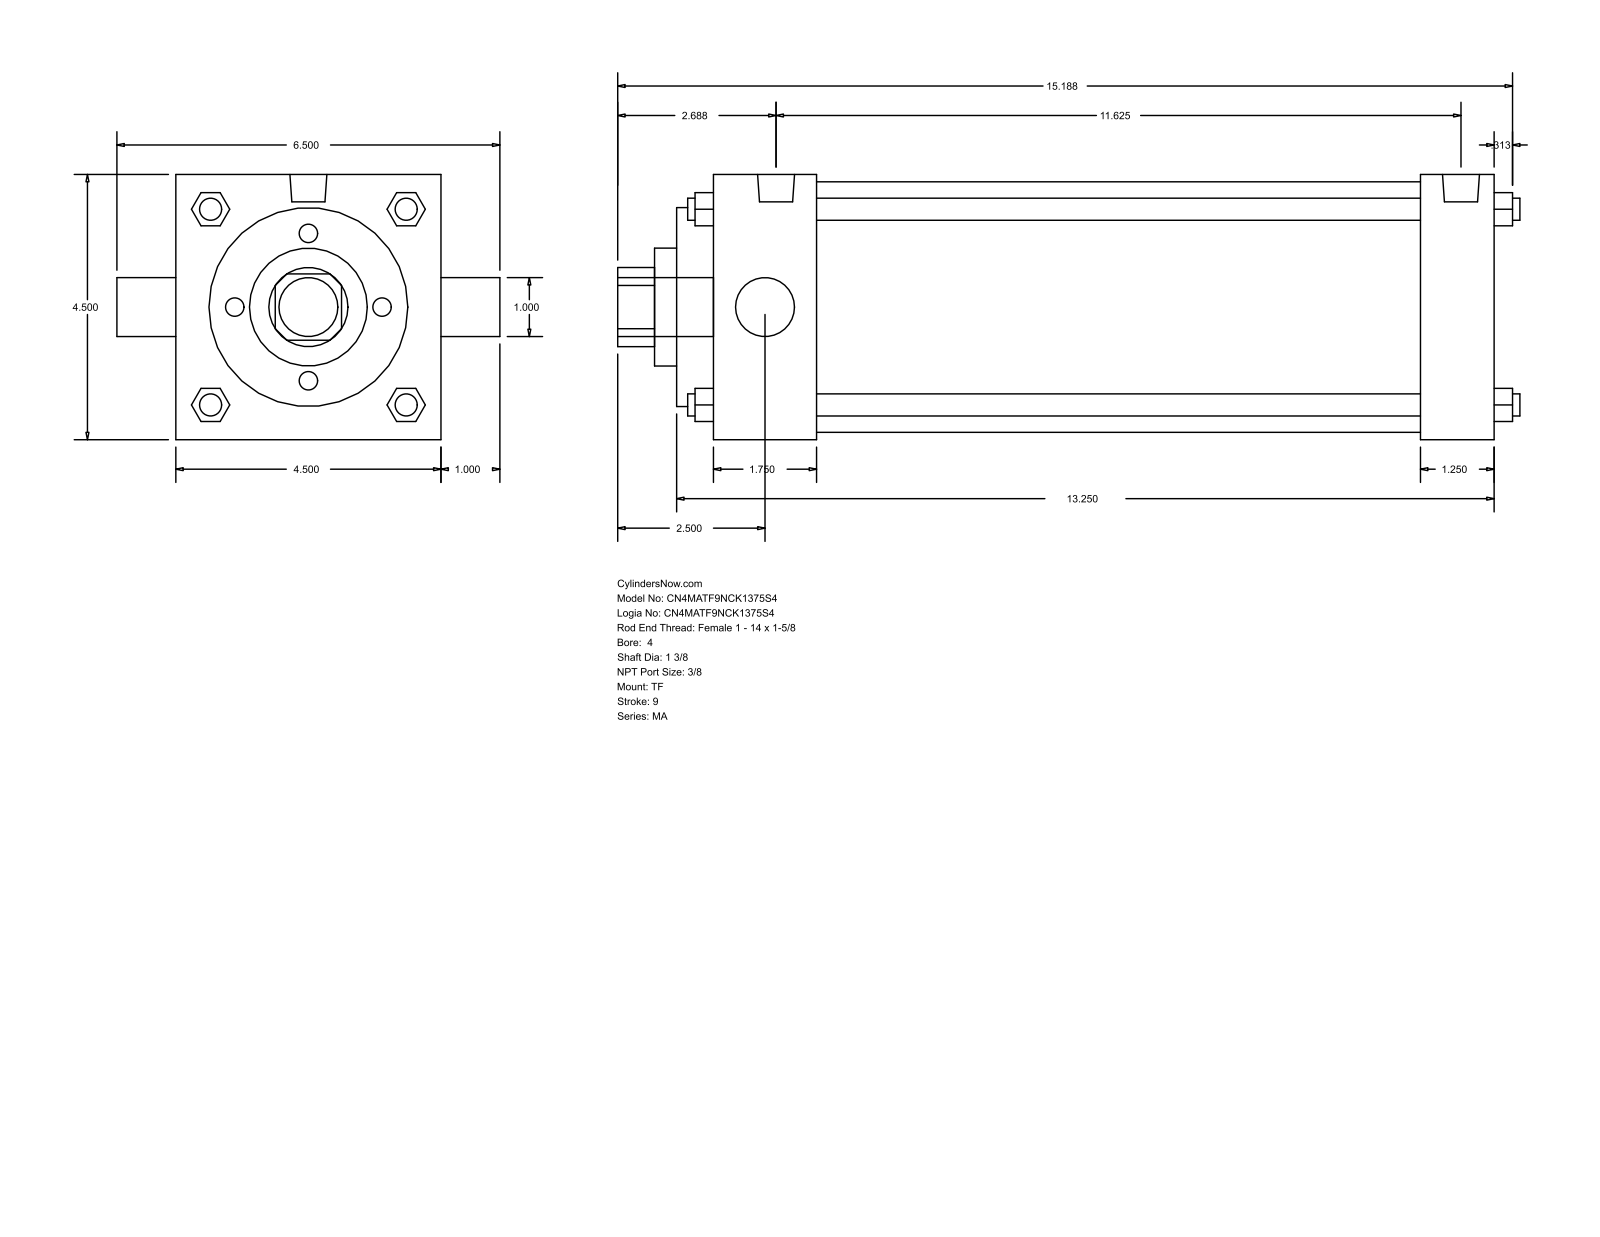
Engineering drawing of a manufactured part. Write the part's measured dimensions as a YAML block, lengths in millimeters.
part_name: "MA_TF__0400_1.375"
step_written_by: "GSSL Pune (CONFIG_CONTROL_DESIGN)"
units: millimeters
bodies: {solids: 0, faces: 122, planar: 93, cylindrical: 29, other: 0}
overall_size: [388.94, 165.1, 114.3]
round_holes:
  - {diameter: 25.4, count: 1}
  - {diameter: 34.92, count: 1}
  - {diameter: 50.8, count: 1}
  - {diameter: 85.72, count: 1}
  - {diameter: 107.95, count: 1}
round_bosses_or_shafts:
  - {diameter: 9.53, count: 4}
  - {diameter: 11.11, count: 3}
  - {diameter: 15.93, count: 2}
  - {diameter: 25.4, count: 1}
partial_cylinders:
  - {radius: 17.06, count: 1}
face_to_face_distances: [114.3, 336.55, 352.42, 15.87, 320.67, 304.8, 31.75, 60.32, 44.45, 260.35]
